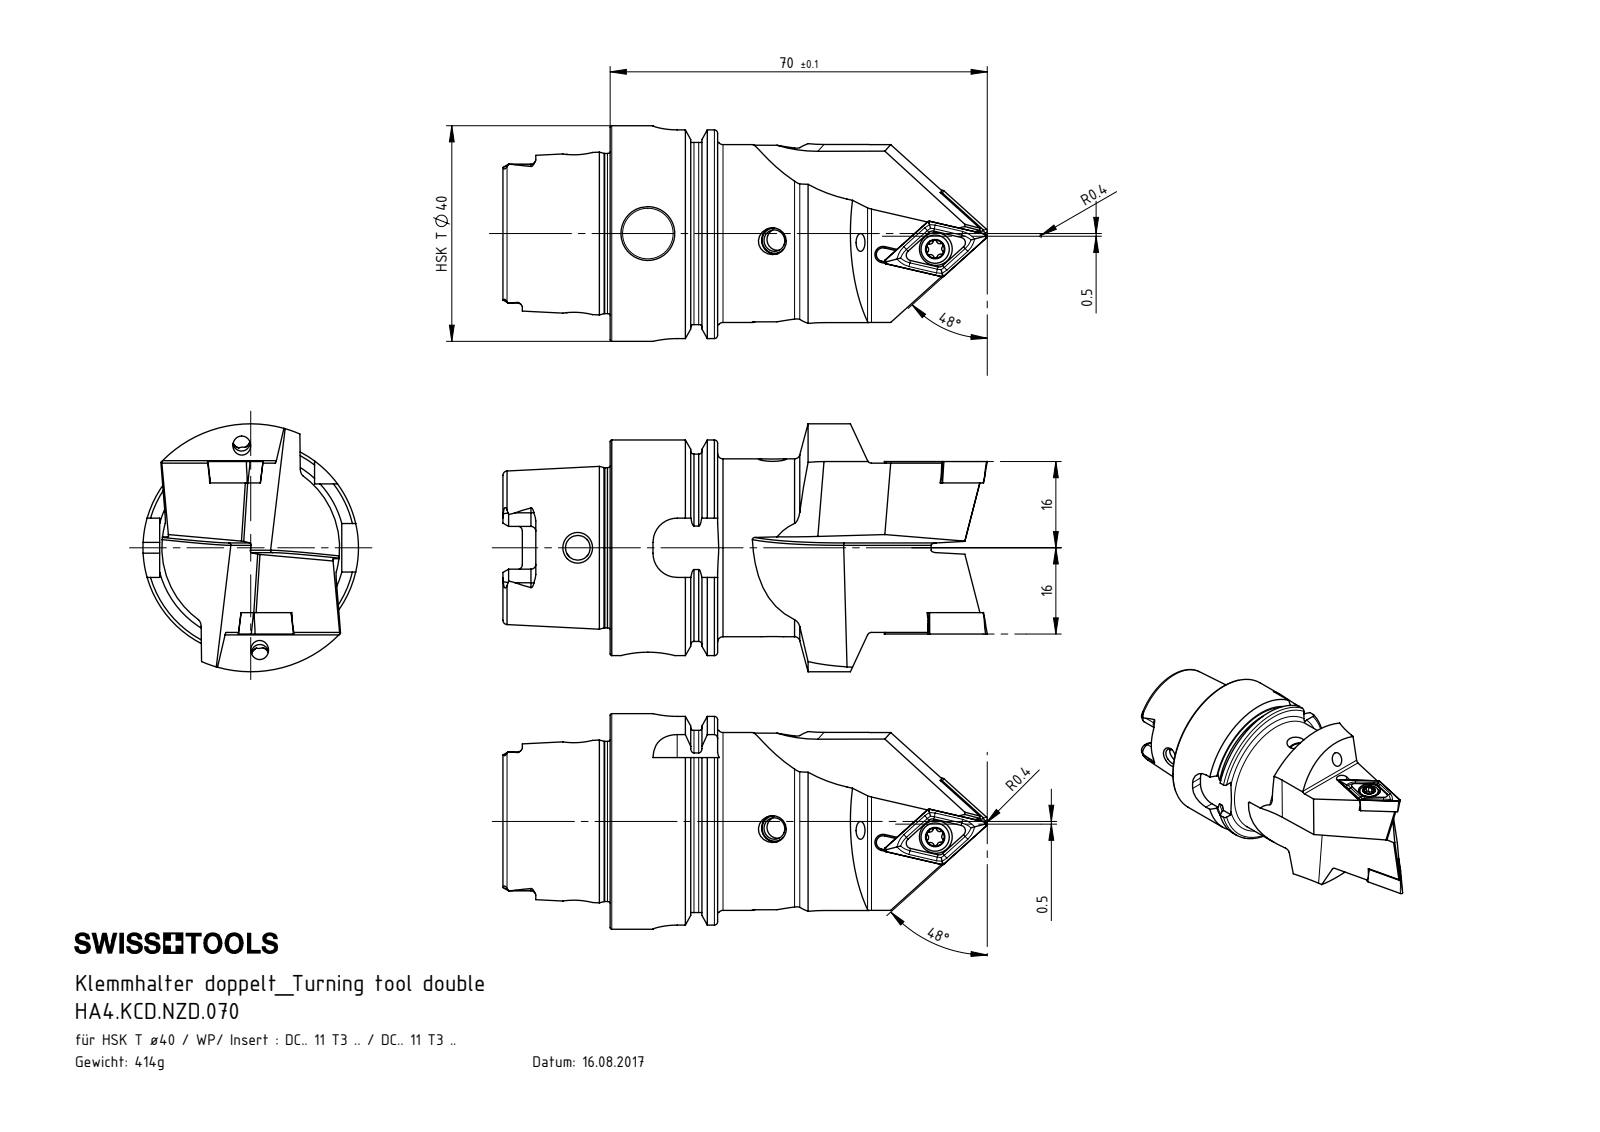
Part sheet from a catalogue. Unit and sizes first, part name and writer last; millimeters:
Units: millimetres
Overall size (bounding box): 89.91 × 46 × 40
Round holes (diameter × count): ⌀3.3 ×4, ⌀5 ×3, ⌀4 ×2, ⌀4.2 ×2, ⌀4.4 ×2, ⌀6.1 ×2, ⌀4.6 ×1, ⌀10 ×1, ⌀11 ×1, ⌀12.5 ×1, ⌀21 ×1, ⌀25.5 ×1
Round bosses / shafts (diameter × count): ⌀5.25 ×2, ⌀5 ×2, ⌀4 ×2, ⌀40 ×1, ⌀34.75 ×1, ⌀33 ×1, ⌀29.71 ×1
Partial cylindrical surfaces — rounded edges, fillets, slot ends (radius × count): R0.34 ×12, R0.59 ×12, R0.9 ×6, R1.88 ×4, R4.5 ×4, R26 ×4, R0.4 ×2, R0.8 ×2
Main face-to-face distances: 3.67, 27.73, 7.95, 19.95, 12, 30, 27.85, 24.06, 31.4, 19.9
Hole centre spacings: 5.77, 53.41, 53.53, 5.74, 5.8
Volume: 52 209 mm³ · Surface area: 17 885 mm²
Bodies: 9 solids, 479 faces (113 planar, 139 cylindrical, 227 other)
Part name (STEP PRODUCT): DCMT11T304; HA4-KCD.NZD.070_A; KVT_MB_600_050; HA4.KCD.NZD.070 (+1 more)
STEP written by: SolidWorks 2017 (AUTOMOTIVE_DESIGN)
